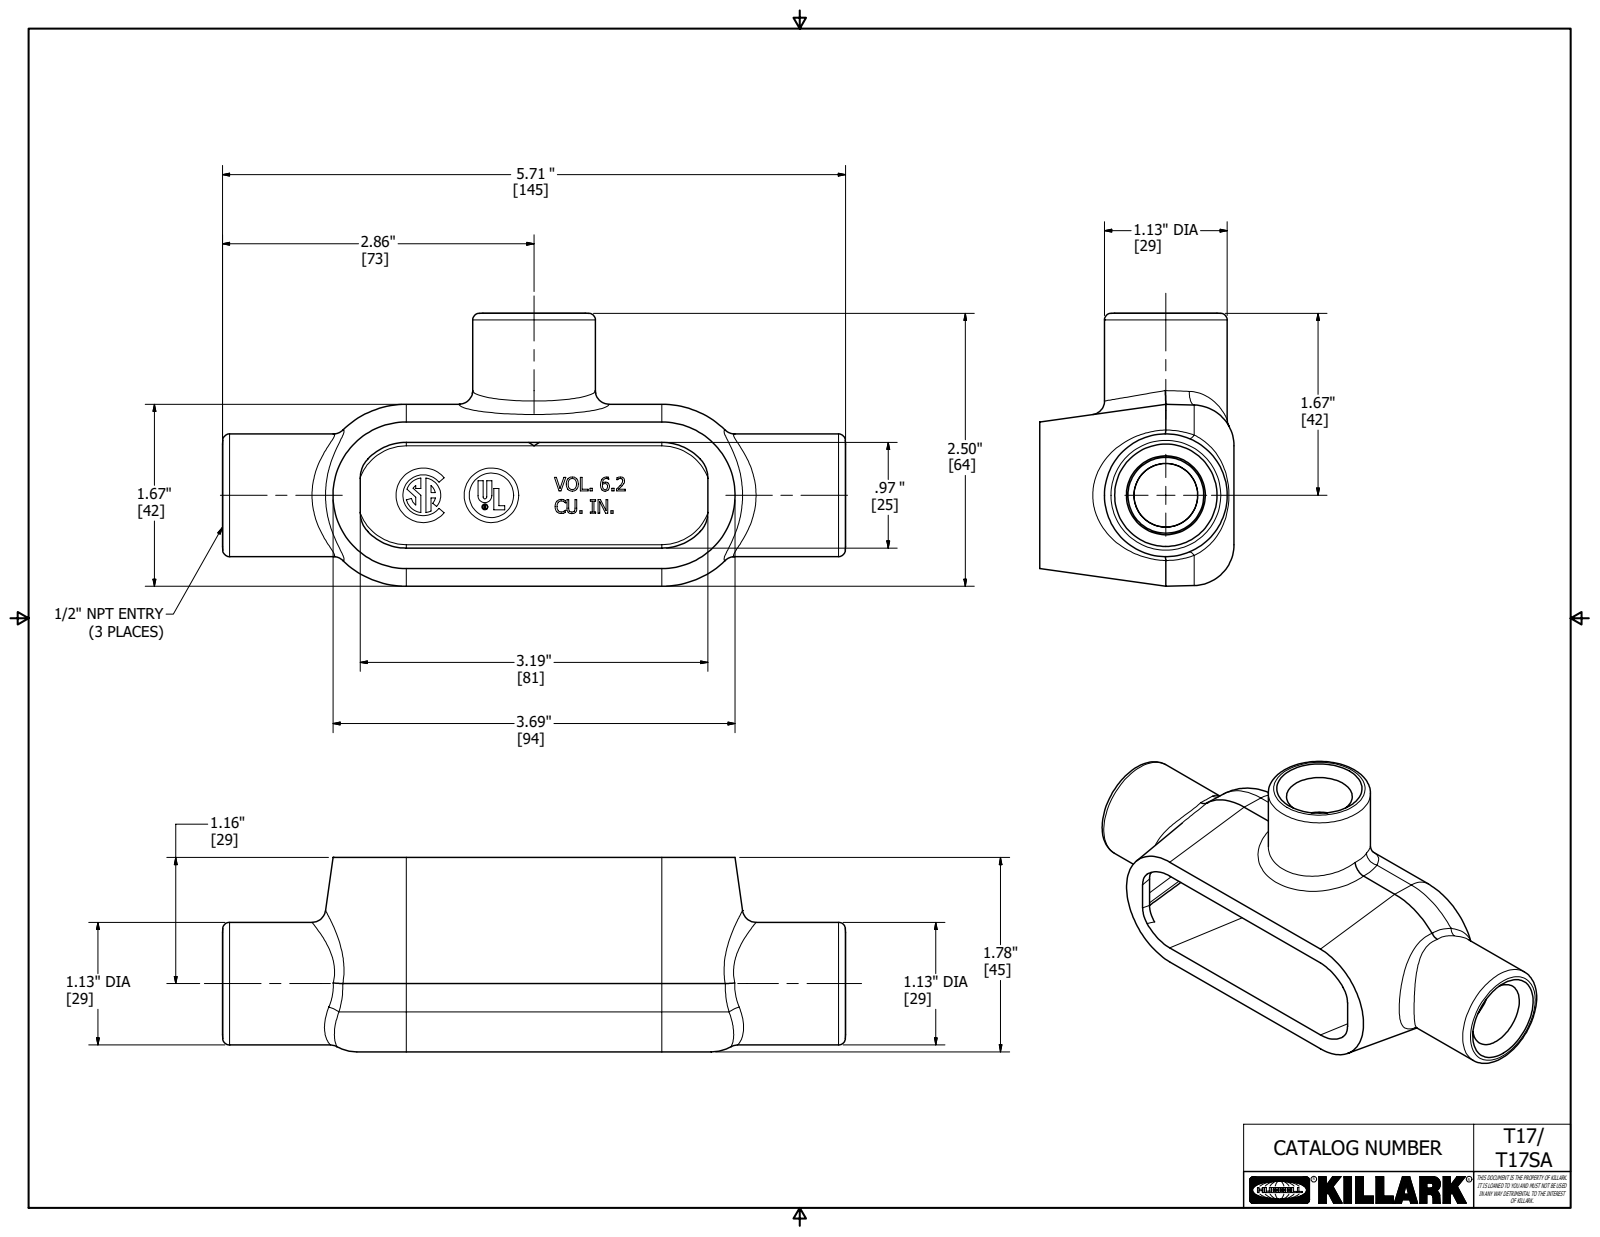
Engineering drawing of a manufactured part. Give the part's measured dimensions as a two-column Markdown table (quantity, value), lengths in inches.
| quantity | value |
| --- | --- |
| part name | 17645-2 |
| STEP written by | Autodesk Inventor 2018 (AUTOMOTIVE_DESIGN) |
| units | inches |
| bodies | 1 solid, 464 faces (268 planar, 41 cylindrical, 155 other) |
| overall size | 5.713 × 2.505 × 1.781 |
| volume | 4.839 in³ |
| surface area | 56.29 in² |
| round holes (diameter × count) | 0.844 × 2, 0.047 × 1, 0.407 × 1, 0.875 × 1 |
| round bosses / shafts (diameter × count) | 1.125 × 2, 0.5 × 1, 0.056 × 1 |
| partial cylindrical surfaces (radius × count) | 0.062 × 4, 0.125 × 4, 0.187 × 3, 0.375 × 2, 0.006 × 1, 0.009 × 1, 0.016 × 1, 0.063 × 1 |
| main face-to-face distances | 0.185, 0.187, 1.781, 1.594, 0.188, 0.031, 0.156, 1.75, 0.219, 1.563 |
| hole center spacings | 0.122 |
